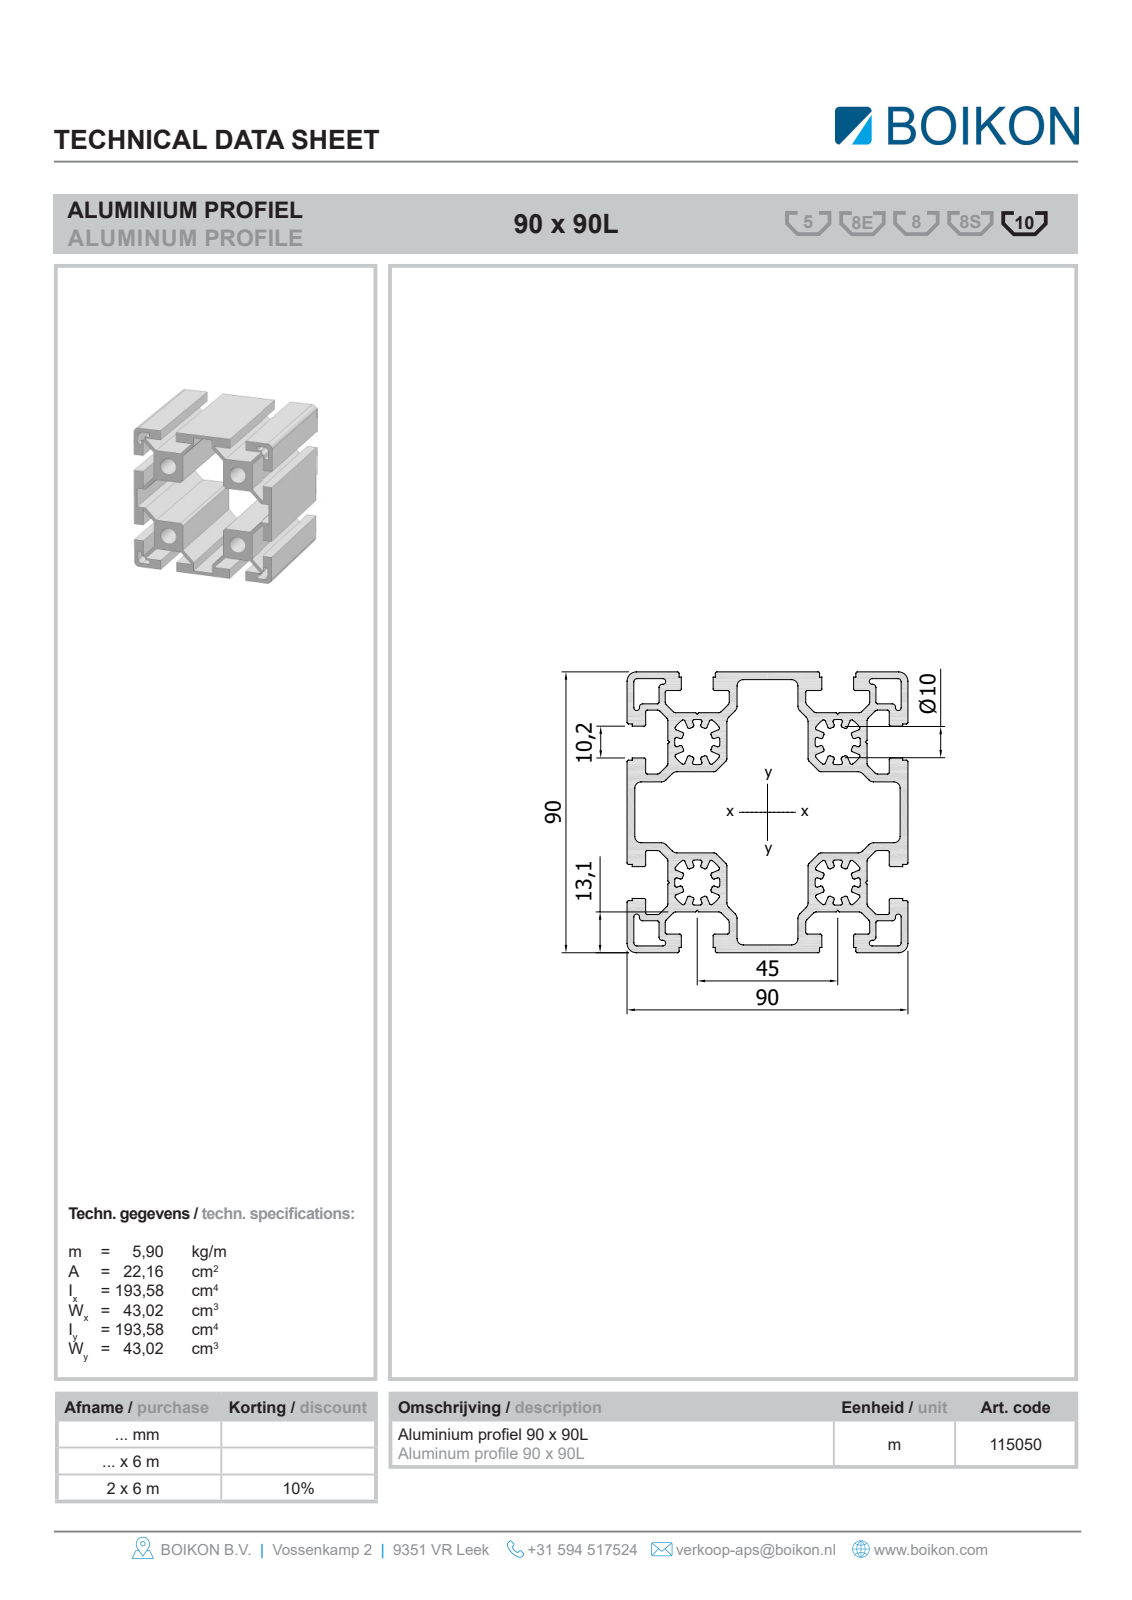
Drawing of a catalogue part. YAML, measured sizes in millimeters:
part_name: "Root; 11505090x90LBOIKON0"
step_written_by: "HiCAD 2013 1802.4 Build 509 (AUTOMOTIVE_DESIGN)"
units: millimeters
bodies: {solids: 1, faces: 142, planar: 126, cylindrical: 16, other: 0}
overall_size: [1000, 90, 90]
volume: 2511000
surface_area: 1369000
round_holes:
  - {diameter: 10.2, count: 4}
partial_cylinders:
  - {radius: 2.5, count: 4}
  - {radius: 3, count: 4}
face_to_face_distances: [45, 7.1, 25.9, 2, 6, 84, 13.1, 76.9, 70.9, 31.9]
hole_center_spacings: [45, 63.64]
